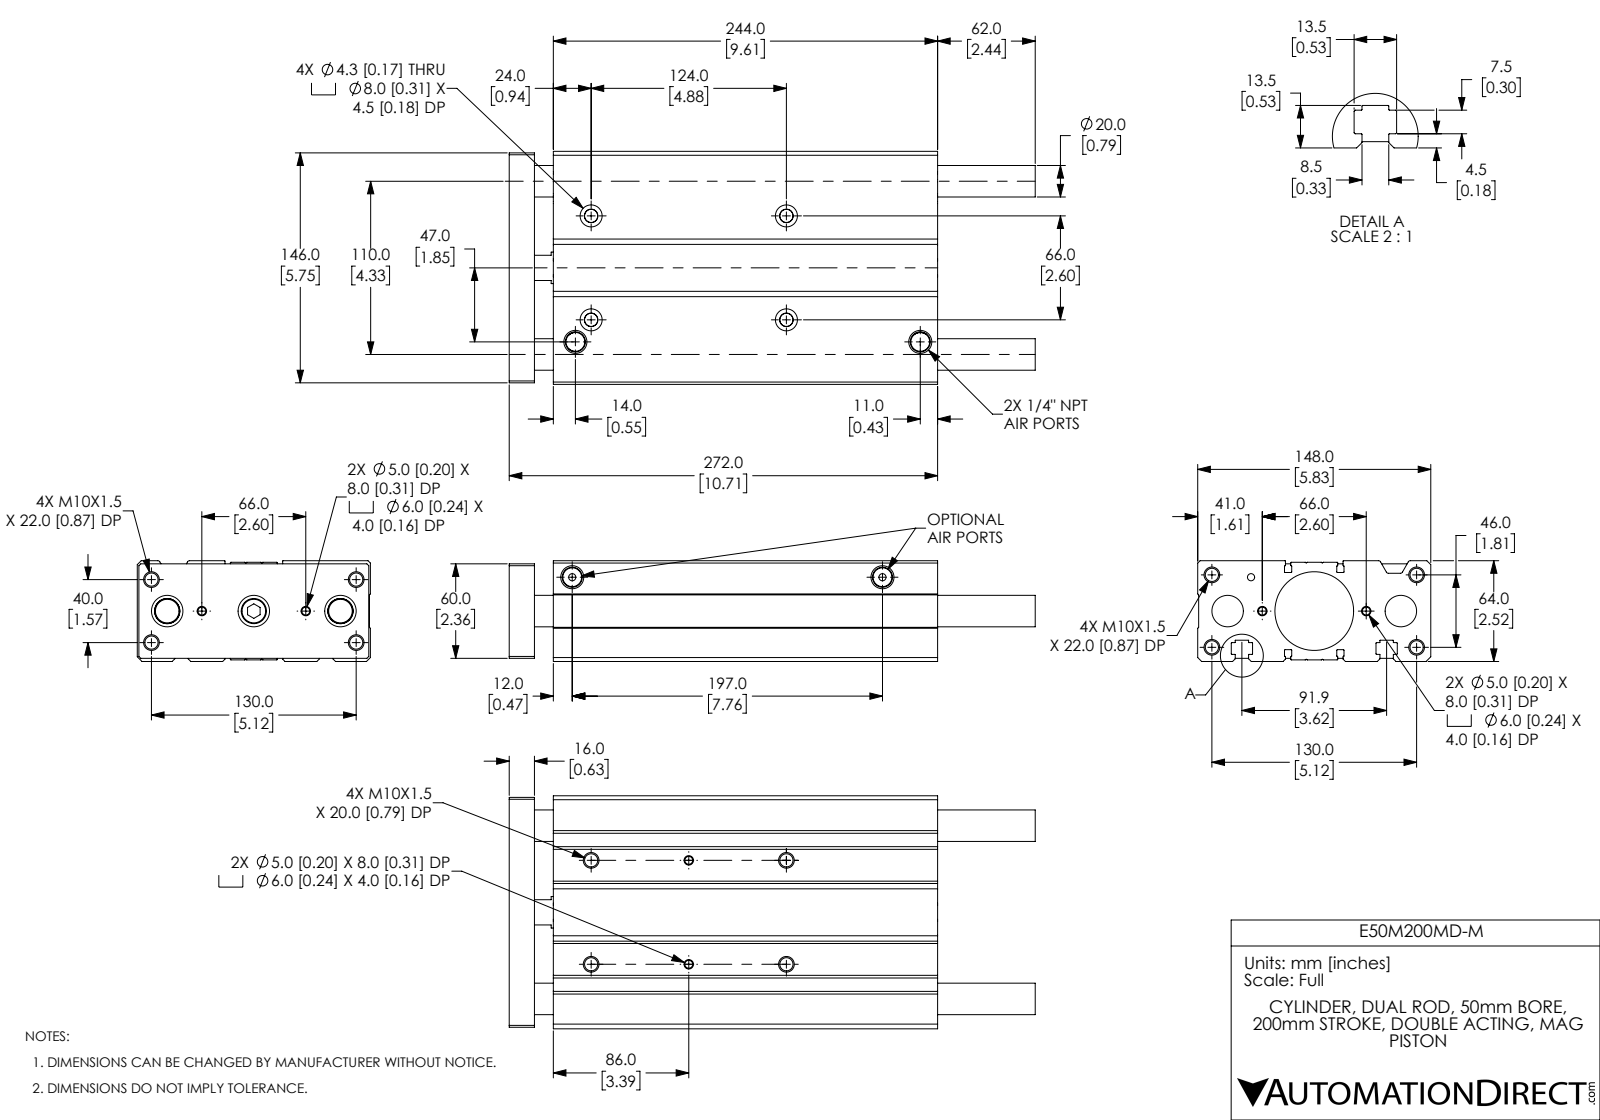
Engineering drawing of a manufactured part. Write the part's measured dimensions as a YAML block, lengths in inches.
part_name: "E50M200MD-M; E50M200MD-M_ENDPLATE; E50M200MD-M_BODY"
step_written_by: "SolidWorks 2019 (CONFIG_CONTROL_DESIGN)"
units: inches
bodies: {solids: 5, faces: 423, planar: 139, cylindrical: 190, other: 94}
overall_size: [13.15, 5.827, 2.52]
volume: 120.6
surface_area: 512.1
round_holes:
  - {diameter: 0.33, count: 12}
  - {diameter: 0.197, count: 4}
  - {diameter: 0.236, count: 4}
  - {diameter: 0.339, count: 4}
  - {diameter: 0.551, count: 4}
  - {diameter: 0.18, count: 3}
  - {diameter: 0.394, count: 3}
  - {diameter: 0.787, count: 3}
  - {diameter: 0.63, count: 2}
  - {diameter: 0.787, count: 1}
  - {diameter: 1.969, count: 1}
  - {diameter: 1.969, count: 1}
round_bosses_or_shafts:
  - {diameter: 0.63, count: 1}
partial_cylinders:
  - {radius: 0.008, count: 32}
  - {radius: 0.016, count: 28}
  - {radius: 0.059, count: 4}
  - {radius: 0.012, count: 2}
face_to_face_distances: [0.039, 2.52, 2.48, 2.441, 0.472, 5.827, 1.102, 0.024, 0.217, 0.63]
hole_center_spacings: [0.118, 0.88, 0.987, 1.486, 1.552, 1.693, 2.441, 2.598]
